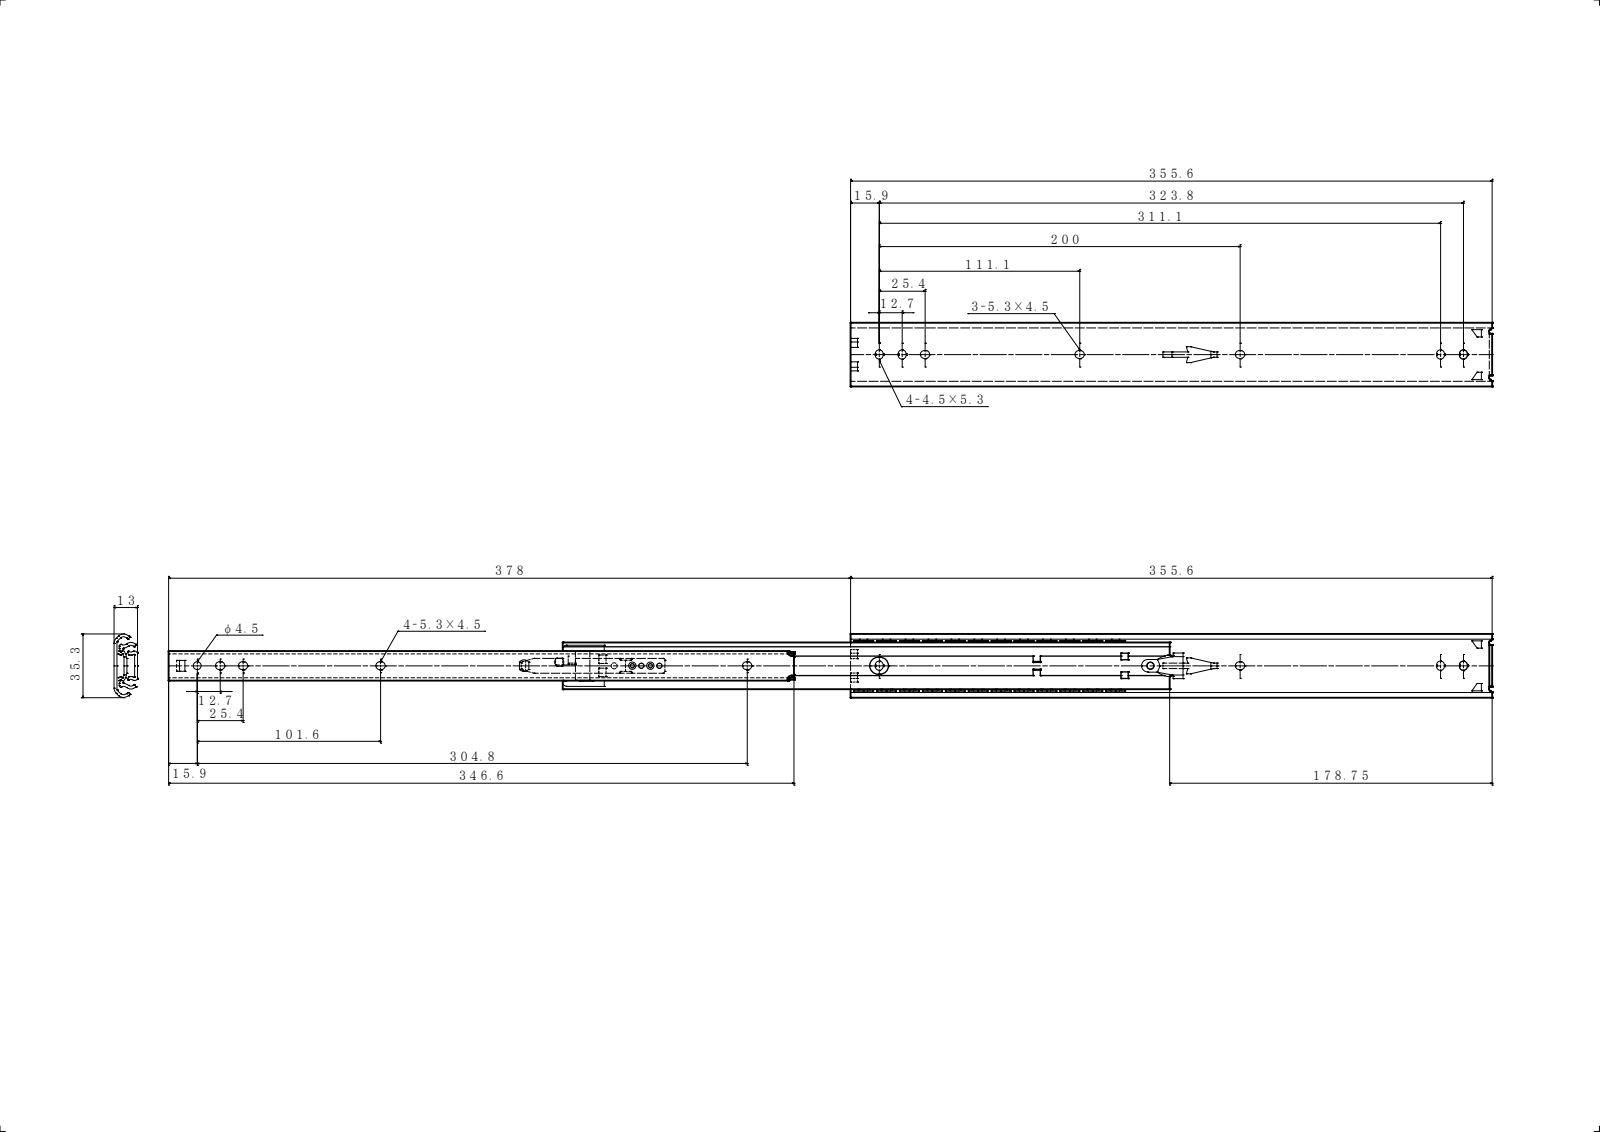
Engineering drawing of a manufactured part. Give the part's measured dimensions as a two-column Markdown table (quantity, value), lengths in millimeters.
| quantity | value |
| --- | --- |
| part name | PN282; PN101; PN65A; C357-14 CM (+5 more) |
| STEP written by | SolidWorks 2019 (CONFIG_CONTROL_DESIGN) |
| units | millimeters |
| bodies | 9 solids, 483 faces (262 planar, 199 cylindrical, 22 other) |
| overall size | 733.6 × 35.3 × 13 |
| volume | 61 897 mm³ |
| surface area | 82 244 mm² |
| round holes (diameter × count) | 1.6 × 2, 2.4 × 2, 2.95 × 2, 3.03 × 2, 4.2 × 2, 4 × 1, 4.5 × 1 |
| round bosses / shafts (diameter × count) | 3.9 × 3, 2.3 × 2, 7 × 1, 2.5 × 1 |
| partial cylindrical surfaces (radius × count) | 2.25 × 22, 0.5 × 15, 2 × 12, 1 × 11, 3 × 10, 0.8 × 8, 0.3 × 4, 1.6 × 4 |
| main face-to-face distances | 1.6, 11.4, 6, 5.4, 13, 9.8, 3.8, 7.6, 4.4, 7 |
| hole center spacings | 5, 10, 4.91, 5.09, 9.91, 10.09, 14.91, 15 |
